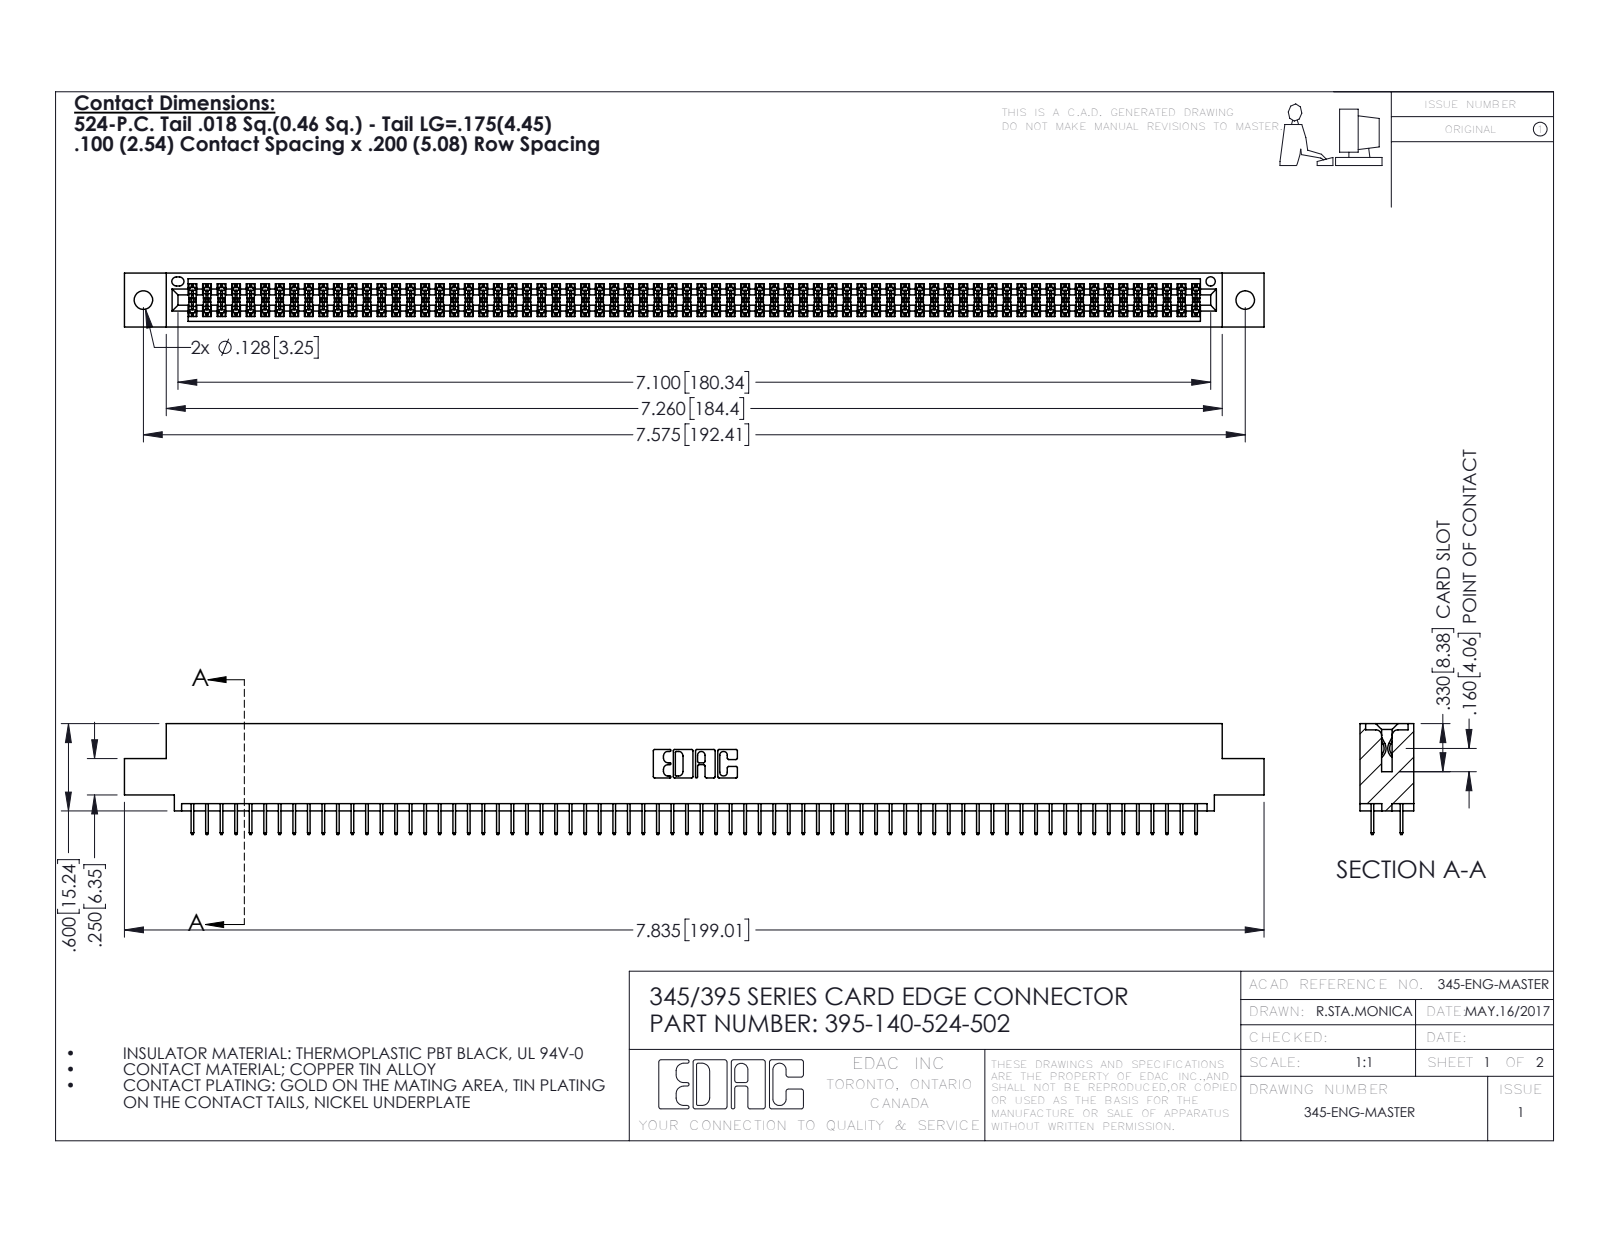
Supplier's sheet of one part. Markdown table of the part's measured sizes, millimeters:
| quantity | value |
| --- | --- |
| part name | 345-292-001_345-293-124; 345 Part_0.110 Offset - 0.128 Dia; 395-140-524-502 |
| STEP written by | SolidWorks 2016 (CONFIG_CONTROL_DESIGN) |
| units | millimeters |
| bodies | 141 solids, 7690 faces (5544 planar, 2146 cylindrical, 0 other) |
| overall size | 199 × 19.4 × 9.4 |
| volume | 19 270 mm³ |
| surface area | 28 290 mm² |
| round holes (diameter × count) | 3.3 × 2, 1.6 × 1 |
| partial cylindrical surfaces (radius × count) | 0.2 × 210, 0.3 × 22, 0.2 × 6, 0.8 × 6, 0.7 × 3, 0.4 × 2, 0.5 × 2, 0.6 × 2 |
| main face-to-face distances | 1.8, 7.6, 5.1, 9.4, 2.5, 6.9, 0.6, 5.7, 1.8, 4.4 |
| hole center spacings | 6.9, 186.4, 192.4 |
